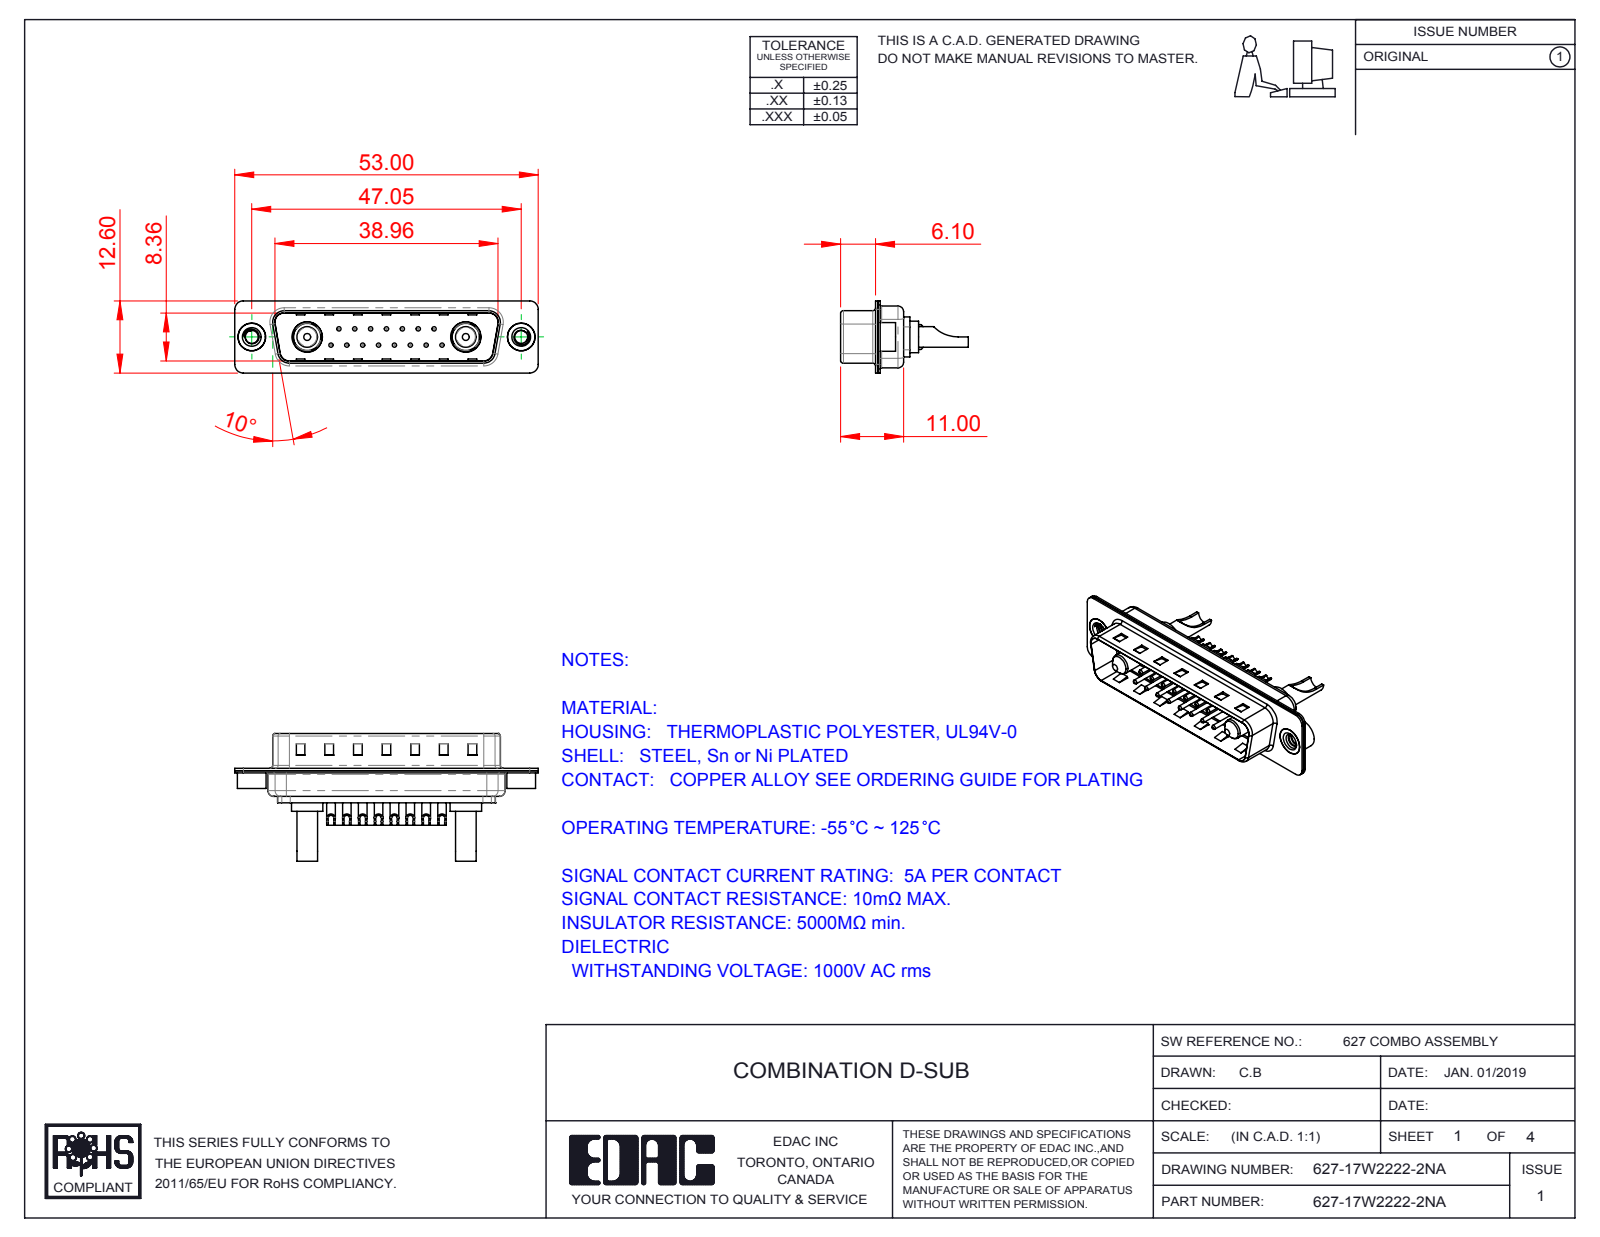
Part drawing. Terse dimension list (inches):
name: 627Combo Contact Row 2_22; Power Pin_20A SC; 627-17W2222-2NA; 627Combo Threaded Rivet_A (+5 more)
written by: SolidWorks 2016 (CONFIG_CONTROL_DESIGN)
unit: in
bodies: 24 solids, 1022 faces (332 planar, 422 cylindrical, 268 other)
size: 2.087 × 0.878 × 0.496
volume: 0.177 in³; area: 10.96 in²
holes: 15× ⌀0.03, 15× ⌀0.039, 15× ⌀0.063, 15× ⌀0.079, 2× ⌀0.089, 2× ⌀0.106, 2× ⌀0.157, 2× ⌀0.189, 2× ⌀0.191, 2× ⌀0.209
bosses: 15× ⌀0.059, 2× ⌀0.217, 2× ⌀0.205, 2× ⌀0.197, 2× ⌀0.193, 2× ⌀0.187, 2× ⌀0.148, 2× ⌀0.142
rounds: 16× R0.059, 12× R0.079, 8× R0.02, 8× R0.063, 6× R0.039, 4× R0.01, 4× R0.024, 4× R0.026
face distances: 0.016, 0.032, 0.377, 0.345, 0.059, 0.22, 0.205, 0.031, 0.048, 0.393
hole spacings: 0.124, 0.109, 0.218, 0.327, 0.198, 0.295, 0.436, 0.198
